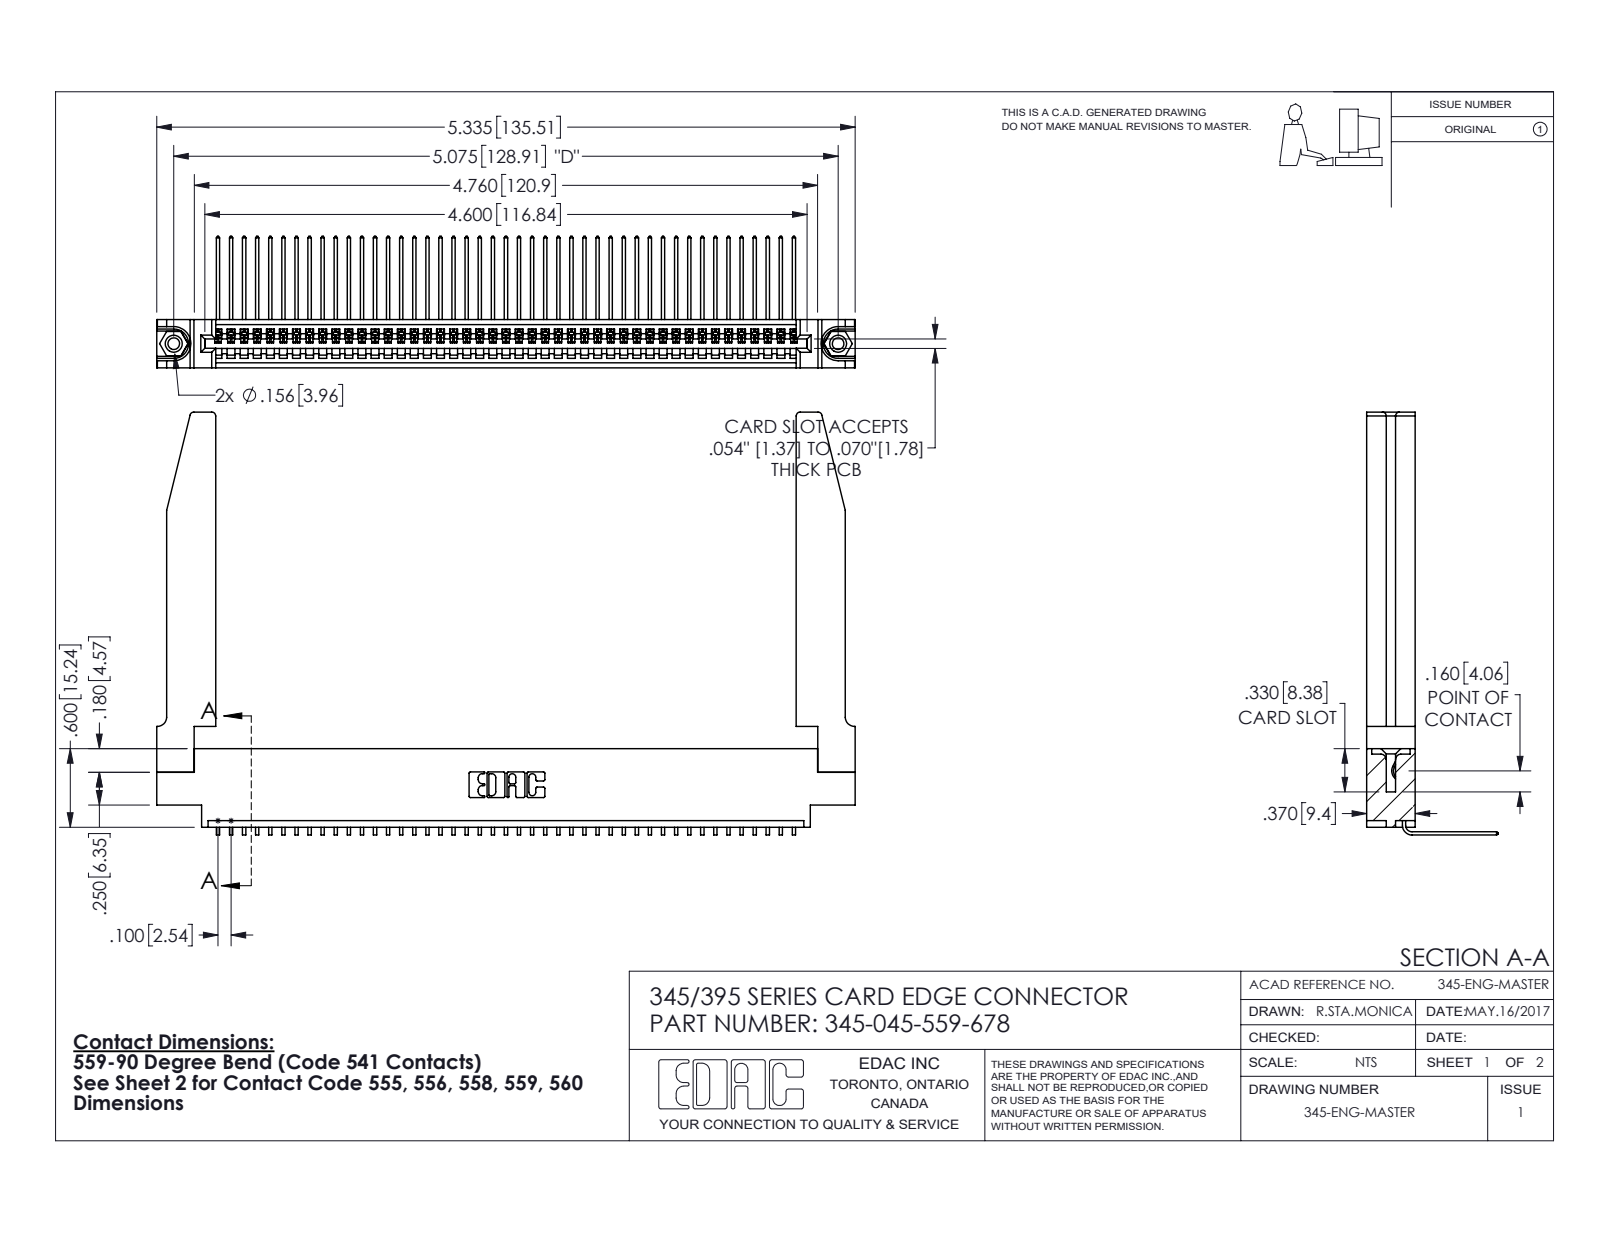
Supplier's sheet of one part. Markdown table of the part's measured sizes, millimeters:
| quantity | value |
| --- | --- |
| part name | 345-250-001_345-250-001-102; 345-292-001_558 559 Tail - 1; 345 Part_0.170 Offset - 0.156 Dia-TH; 345-045-559-678 (+1 more) |
| STEP written by | SolidWorks 2016 (CONFIG_CONTROL_DESIGN) |
| units | millimeters |
| bodies | 50 solids, 3064 faces (2116 planar, 896 cylindrical, 52 other) |
| overall size | 135.5 × 82 × 25.5 |
| volume | 20 700 mm³ |
| surface area | 25 080 mm² |
| round holes (diameter × count) | 2.3 × 2, 3.2 × 2, 4 × 2, 1.6 × 1 |
| round bosses / shafts (diameter × count) | 3.9 × 2 |
| partial cylindrical surfaces (radius × count) | 0.2 × 90, 0.3 × 22, 0.8 × 8, 0.2 × 6, 0.8 × 6, 0.7 × 3, 0.8 × 2, 1 × 2 |
| main face-to-face distances | 9.4, 1.8, 7.6, 2.5, 6.9, 0.6, 5.1, 5.7, 3.8, 3.8 |
| hole center spacings | 6.9, 122.9, 128.9 |
